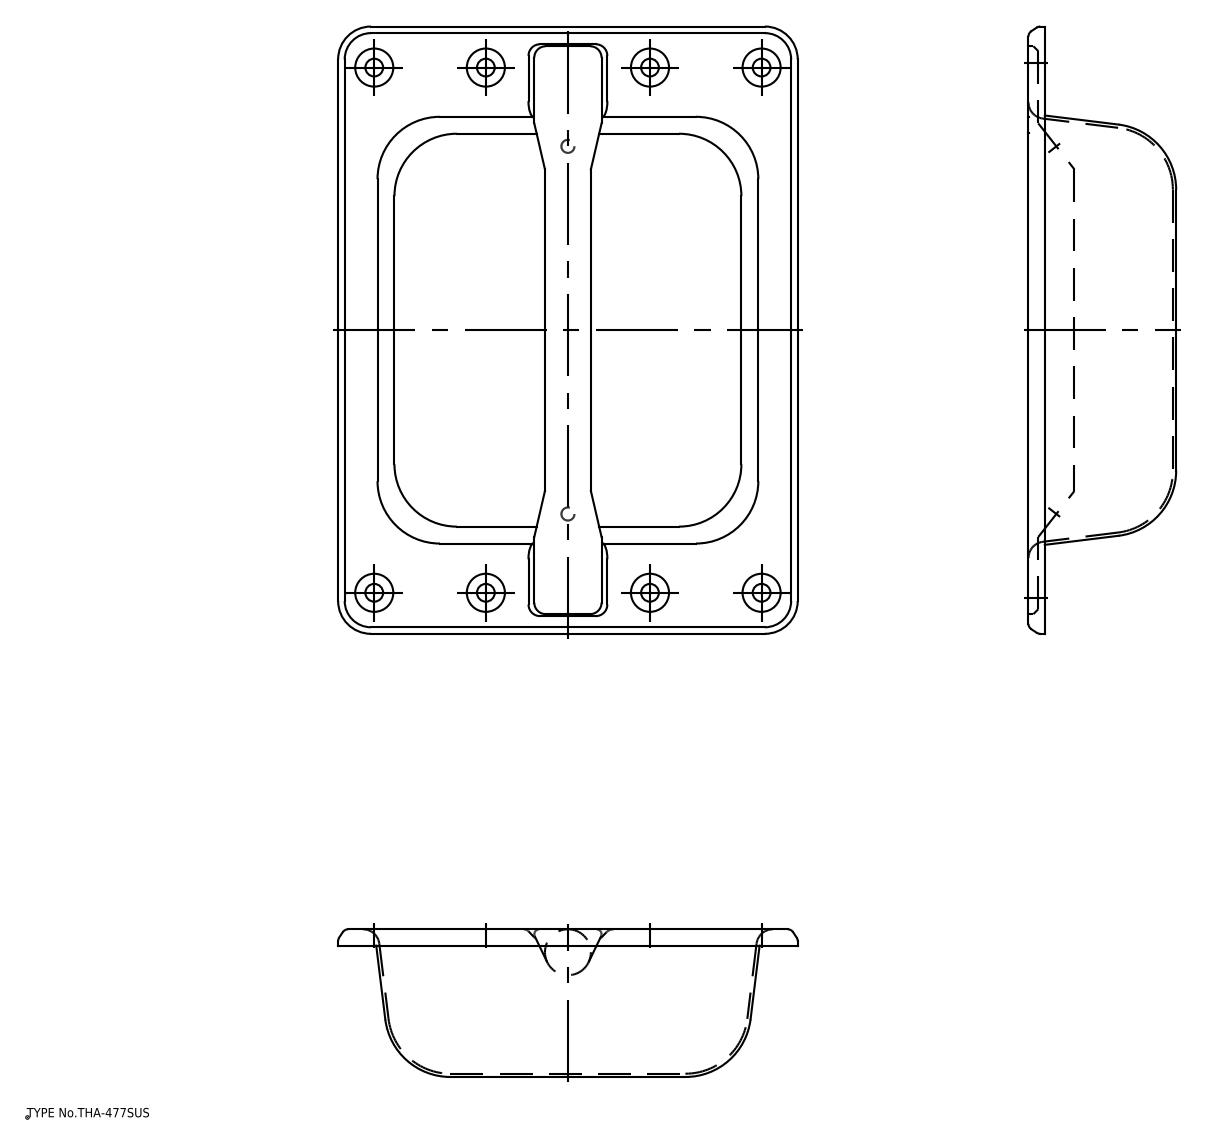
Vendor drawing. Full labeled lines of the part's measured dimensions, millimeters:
STEP written by: spGate 20.6.3 (****-****-****-****) (AUTOMOTIVE_DESIGN)
Units: millimetres
Bodies: 1 solid, 389 faces (71 planar, 138 cylindrical, 180 other)
Overall size (bounding box): 185 × 140 × 45
Volume: 62 128 mm³ · Surface area: 90 219 mm²
Round holes (diameter × count): ⌀5.3 ×8
Round bosses / shafts (diameter × count): ⌀7.3 ×8, ⌀13.8 ×1
Partial cylindrical surfaces — rounded edges, fillets, slot ends (radius × count): R1 ×16, R1.5 ×12, R0.5 ×10, R2 ×8, R3.5 ×8, R19 ×8, R20 ×8, R2.5 ×4
Main face-to-face distances: 1, 44, 43, 45, 0.7, 4, 1.01, 3.3, 40.7, 43.7
Hole centre spacings: 34, 84, 160, 163.57, 180.71, 50, 118, 167.63
